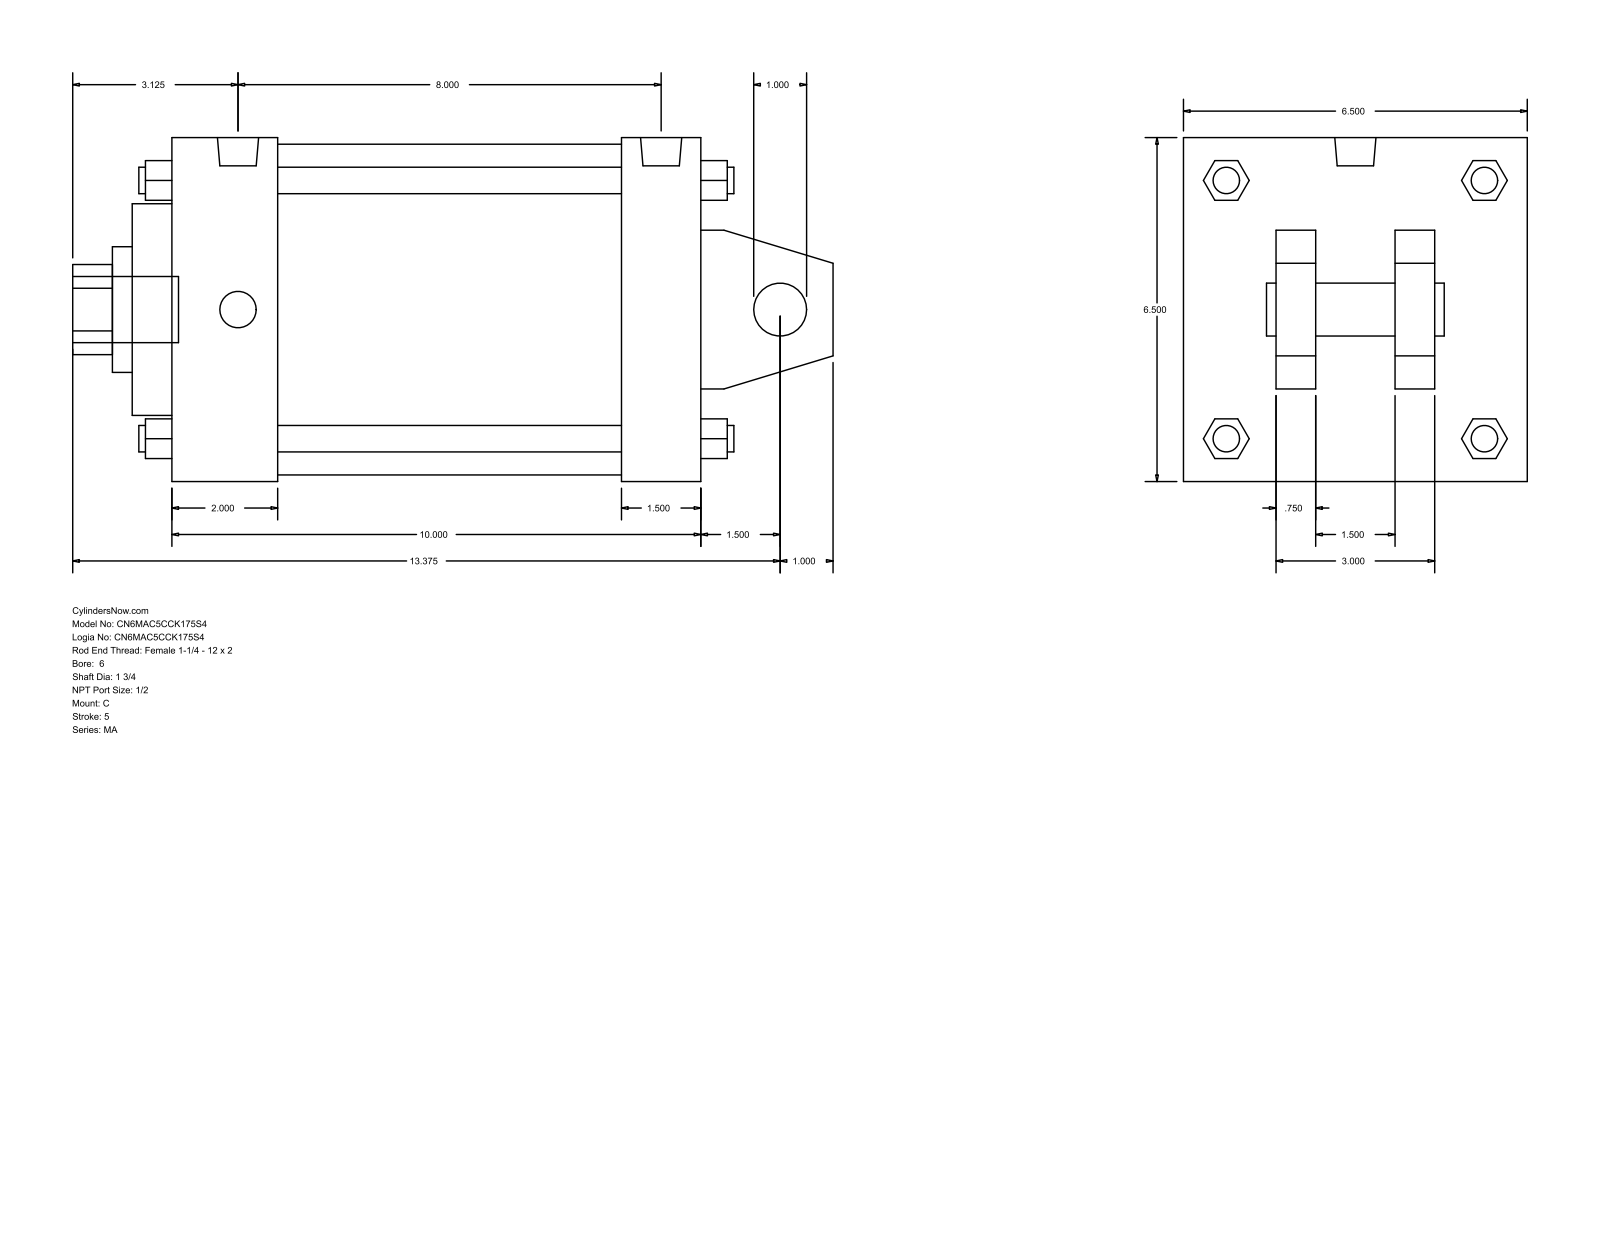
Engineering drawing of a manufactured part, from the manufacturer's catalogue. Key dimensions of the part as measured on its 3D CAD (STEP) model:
Part name (STEP PRODUCT): MA_C__0600_1.75
STEP written by: GSSL Pune (CONFIG_CONTROL_DESIGN)
Units: millimetres
Bodies: 0 solids, 141 faces (109 planar, 32 cylindrical, 0 other)
Overall size (bounding box): 365.12 × 165.1 × 165.1
Round holes (diameter × count): ⌀25.4 ×1, ⌀44.45 ×1, ⌀60.33 ×1, ⌀101.6 ×1, ⌀158.75 ×1
Round bosses / shafts (diameter × count): ⌀17.46 ×4, ⌀12.7 ×4, ⌀19.77 ×2, ⌀31.75 ×1
Partial cylindrical surfaces — rounded edges, fillets, slot ends (radius × count): R21.63 ×1
Main face-to-face distances: 165.1, 254, 19.05, 38.1, 63.5, 101.6, 50.8, 120.65, 44.45, 215.9
